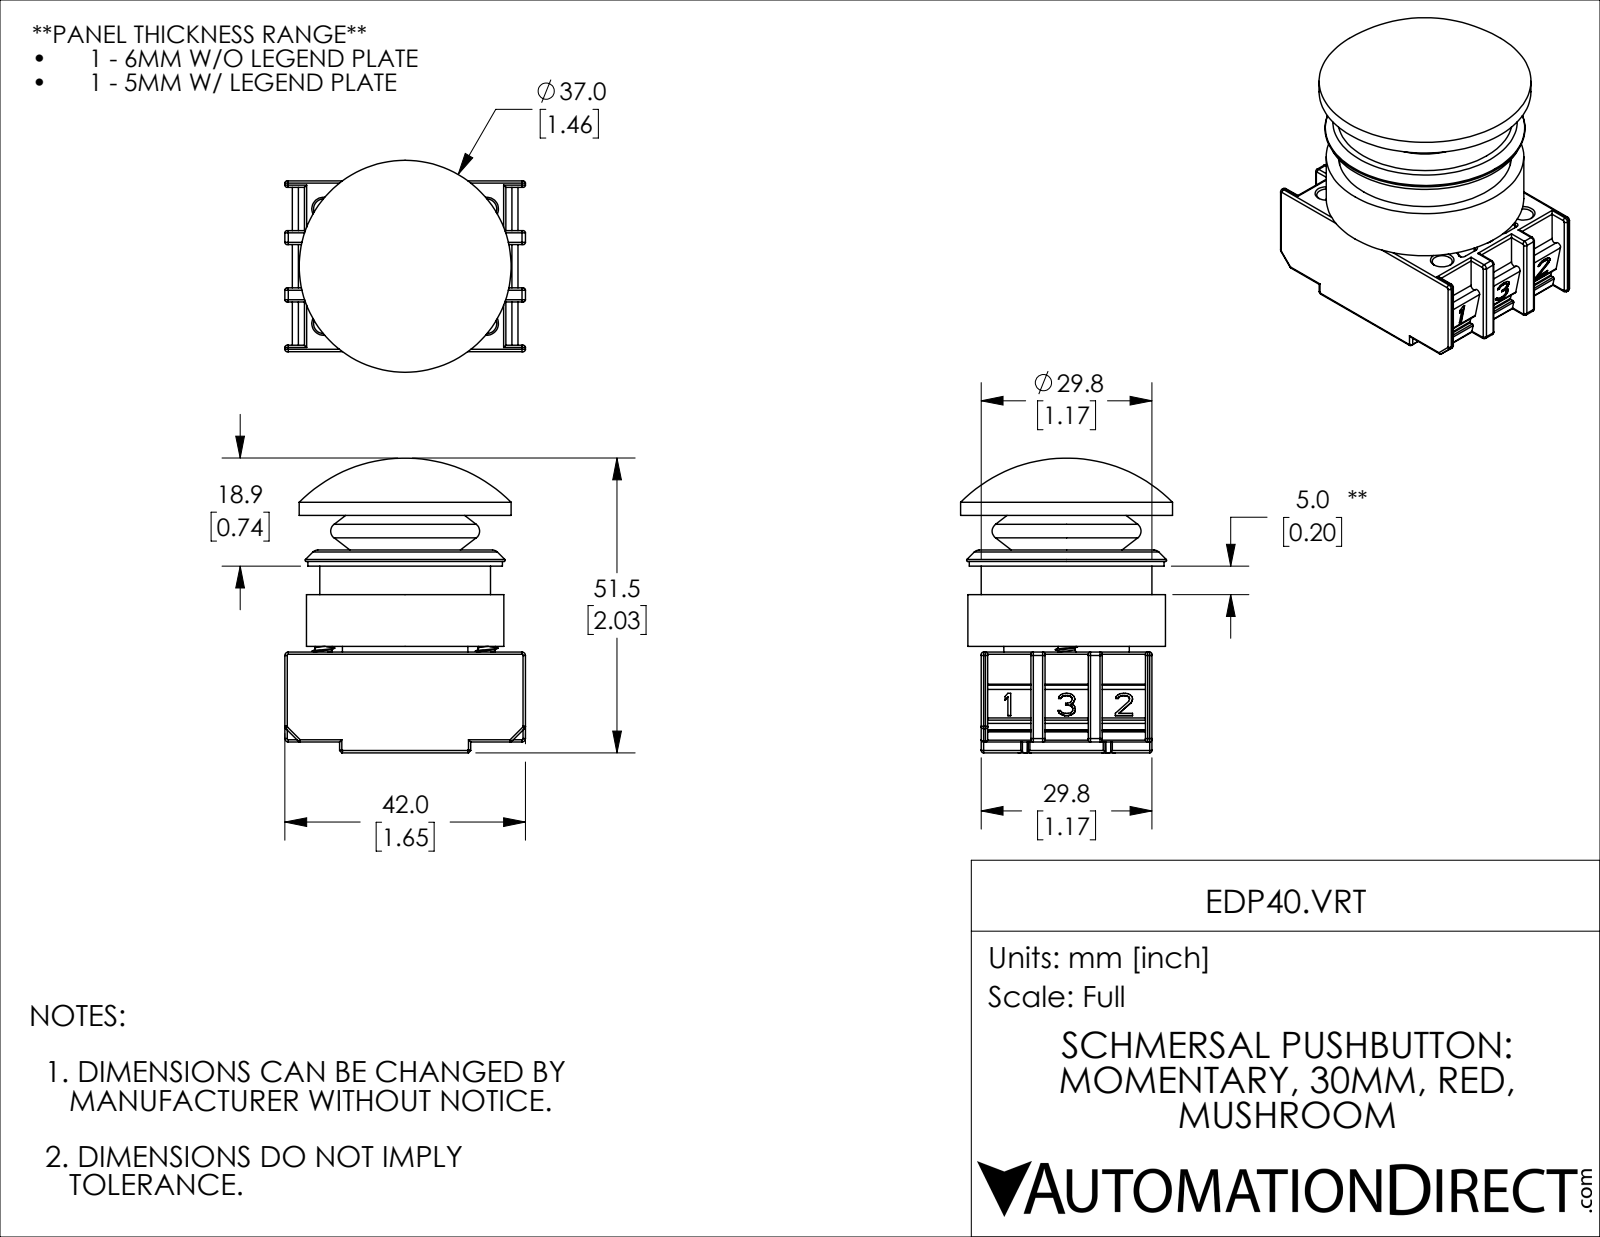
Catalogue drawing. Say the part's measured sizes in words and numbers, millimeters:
The part is named "EDP40.VRT". Its 3-D file was written by "SolidWorks 2019 (CONFIG_CONTROL_DESIGN)". It is 5 solids with 1490 faces: 538 planar, 503 cylindrical and 449 other. Overall it measures 51.45 by 42 by 37 millimeters. Its volume is 32 755 cubic millimeters and its surface area 23 609 square millimeters. Round holes: 6 of diameter 3.5, 6 of diameter 5.15, 1 of diameter 8.25, 1 of diameter 12.15, 1 of diameter 18.8, 1 of diameter 19.5, 1 of diameter 24.1, 1 of diameter 24.2, 1 of diameter 26, 1 of diameter 30.2, 1 of diameter 32. Round bosses or shafts: 2 of diameter 4.8, 2 of diameter 2.93, 1 of diameter 37, 1 of diameter 34.5, 1 of diameter 34, 1 of diameter 29.8, 1 of diameter 25.5, 1 of diameter 24. Partial cylindrical surfaces (rounded edges, fillets, slot ends): 112 of radius 0.4, 48 of radius 0.3, 28 of radius 0.2, 8 of radius 0.6, 6 of radius 0.5, 6 of radius 0.8, 2 of radius 0.1, 2 of radius 0.6. The main face-to-face distances are 18.6, 29.8, 1, 1.9, 16.8, 17.6, 35.4, 17.8, 20.95, 10. The hole center spacings are 10, 17.41, 30.2, 28.5, 14.25, 20, 34.82.
